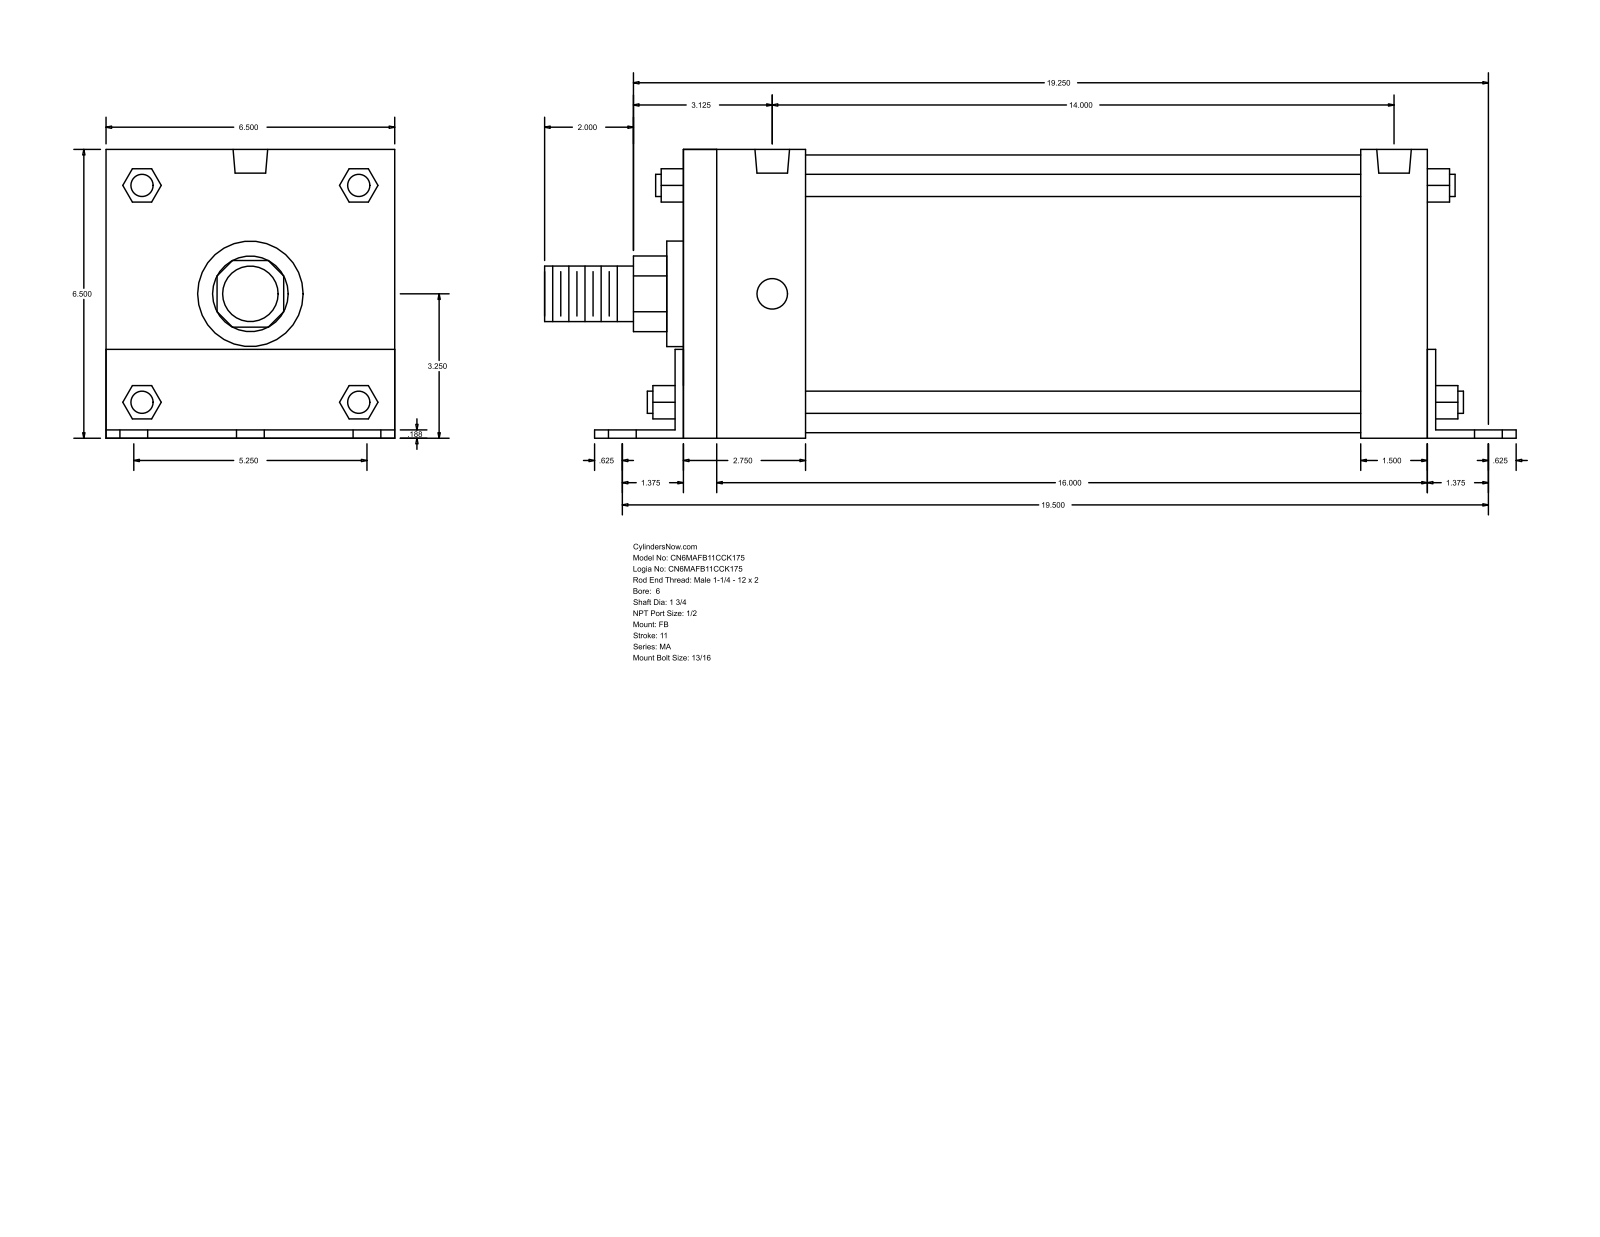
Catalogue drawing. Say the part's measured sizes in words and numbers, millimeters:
The part is named "MA_FB__0600_1.75". Its 3-D file was written by "GSSL Pune (CONFIG_CONTROL_DESIGN)". It is 0 solids with 140 faces: 105 planar, 35 cylindrical and 0 other. Overall it measures 555.62 by 165.15 by 165.1 millimeters. Round holes: 6 of diameter 20.64, 4 of diameter 17.46, 2 of diameter 19.77. Round bosses or shafts: 4 of diameter 12.7, 1 of diameter 158.75, 1 of diameter 60.33, 1 of diameter 44.45, 1 of diameter 31.75. Partial cylindrical surfaces (rounded edges, fillets, slot ends): 1 of radius 21.63, 1 of radius 32.05. The main face-to-face distances are 165.1, 4.76, 425.45, 165.15, 4.71, 160.39, 69.85, 74.61, 4.77, 38.09. The hole center spacings are 66.67, 499.77, 495.3, 85.78, 108.6, 133.34, 355.6, 414.96.
